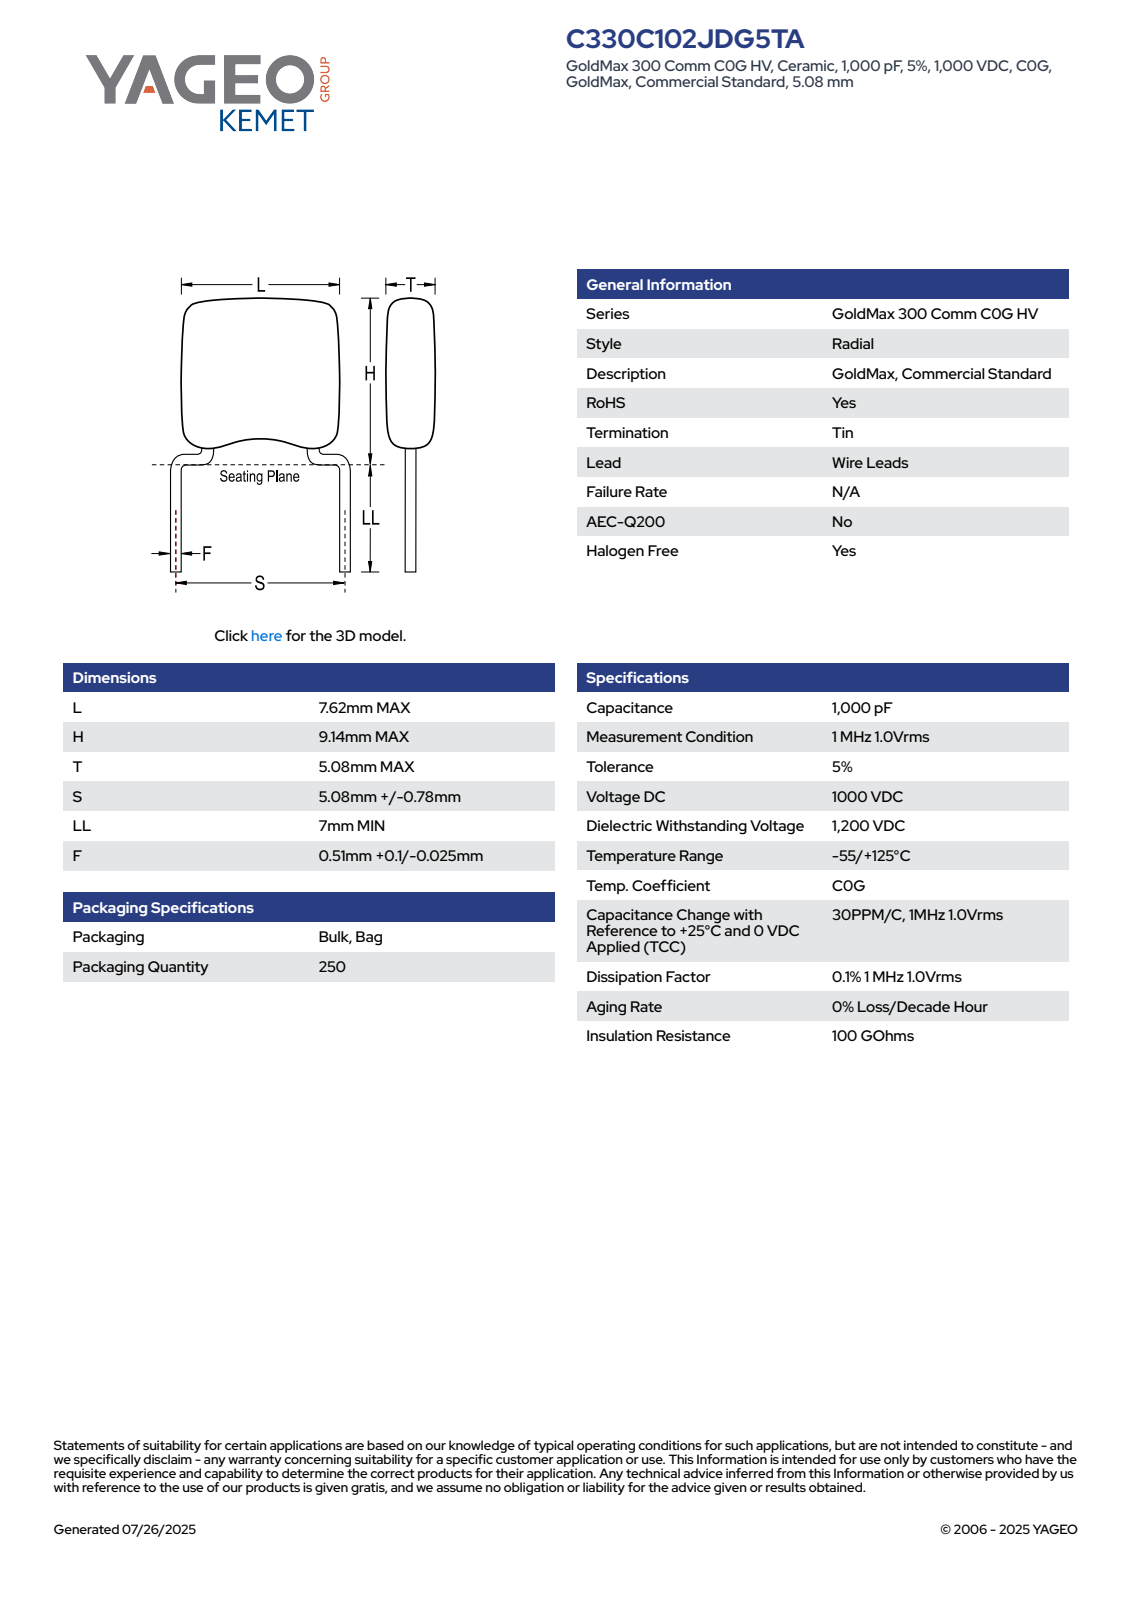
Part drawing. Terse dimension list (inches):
name: CCR_SB_7.62X9.14_L7.62H9.14T5.08S5.08LL7F0.51
written by: SolidWorks 2014 (AUTOMOTIVE_DESIGN)
unit: in
bodies: 4 solids, 97 faces (65 planar, 14 cylindrical, 18 other)
size: 0.635 × 0.3 × 0.2
volume: 0.016 in³; area: 0.408 in²
bosses: 2× ⌀0.02
rounds: 10× R0.039
face distances: 0.2, 0.3, 0.284, 0.026, 0.156, 0.128, 0.13, 0.154, 0.016, 0.052
